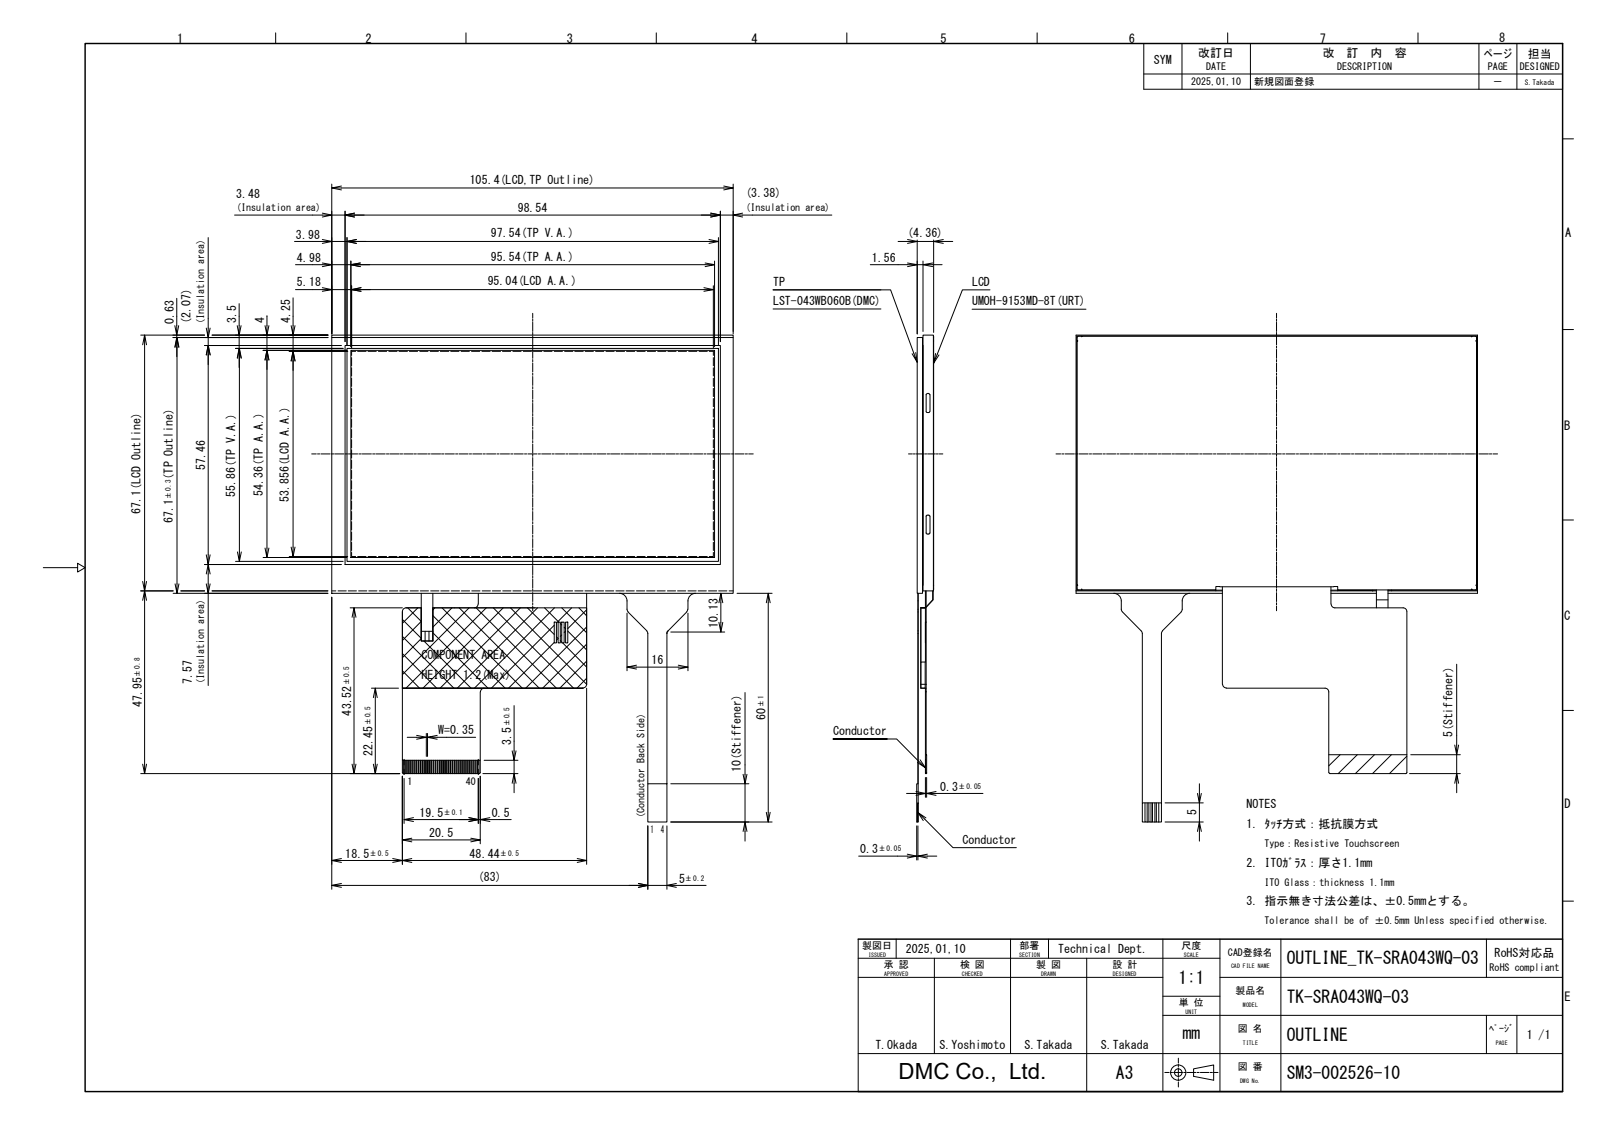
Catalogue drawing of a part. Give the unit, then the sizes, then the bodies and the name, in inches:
Units: inches
Overall size (bounding box): 5.029 × 4.15 × 0.176
Partial cylindrical surfaces — rounded edges, fillets, slot ends (radius × count): R0.012 ×42, R0.039 ×8, R0.02 ×6, R0.079 ×2
Main face-to-face distances: 0.049, 0.055, 0.172, 0.069, 0.117, 0.067, 0.122, 0.047, 0.059, 0.061
Volume: 1.797 in³ · Surface area: 75.84 in²
Bodies: 1 solid, 619 faces (547 planar, 72 cylindrical, 0 other)
Part name (STEP PRODUCT): HP_TK-SRA043WQ-03
STEP written by: Autodesk Inventor 2020 (AUTOMOTIVE_DESIGN)
